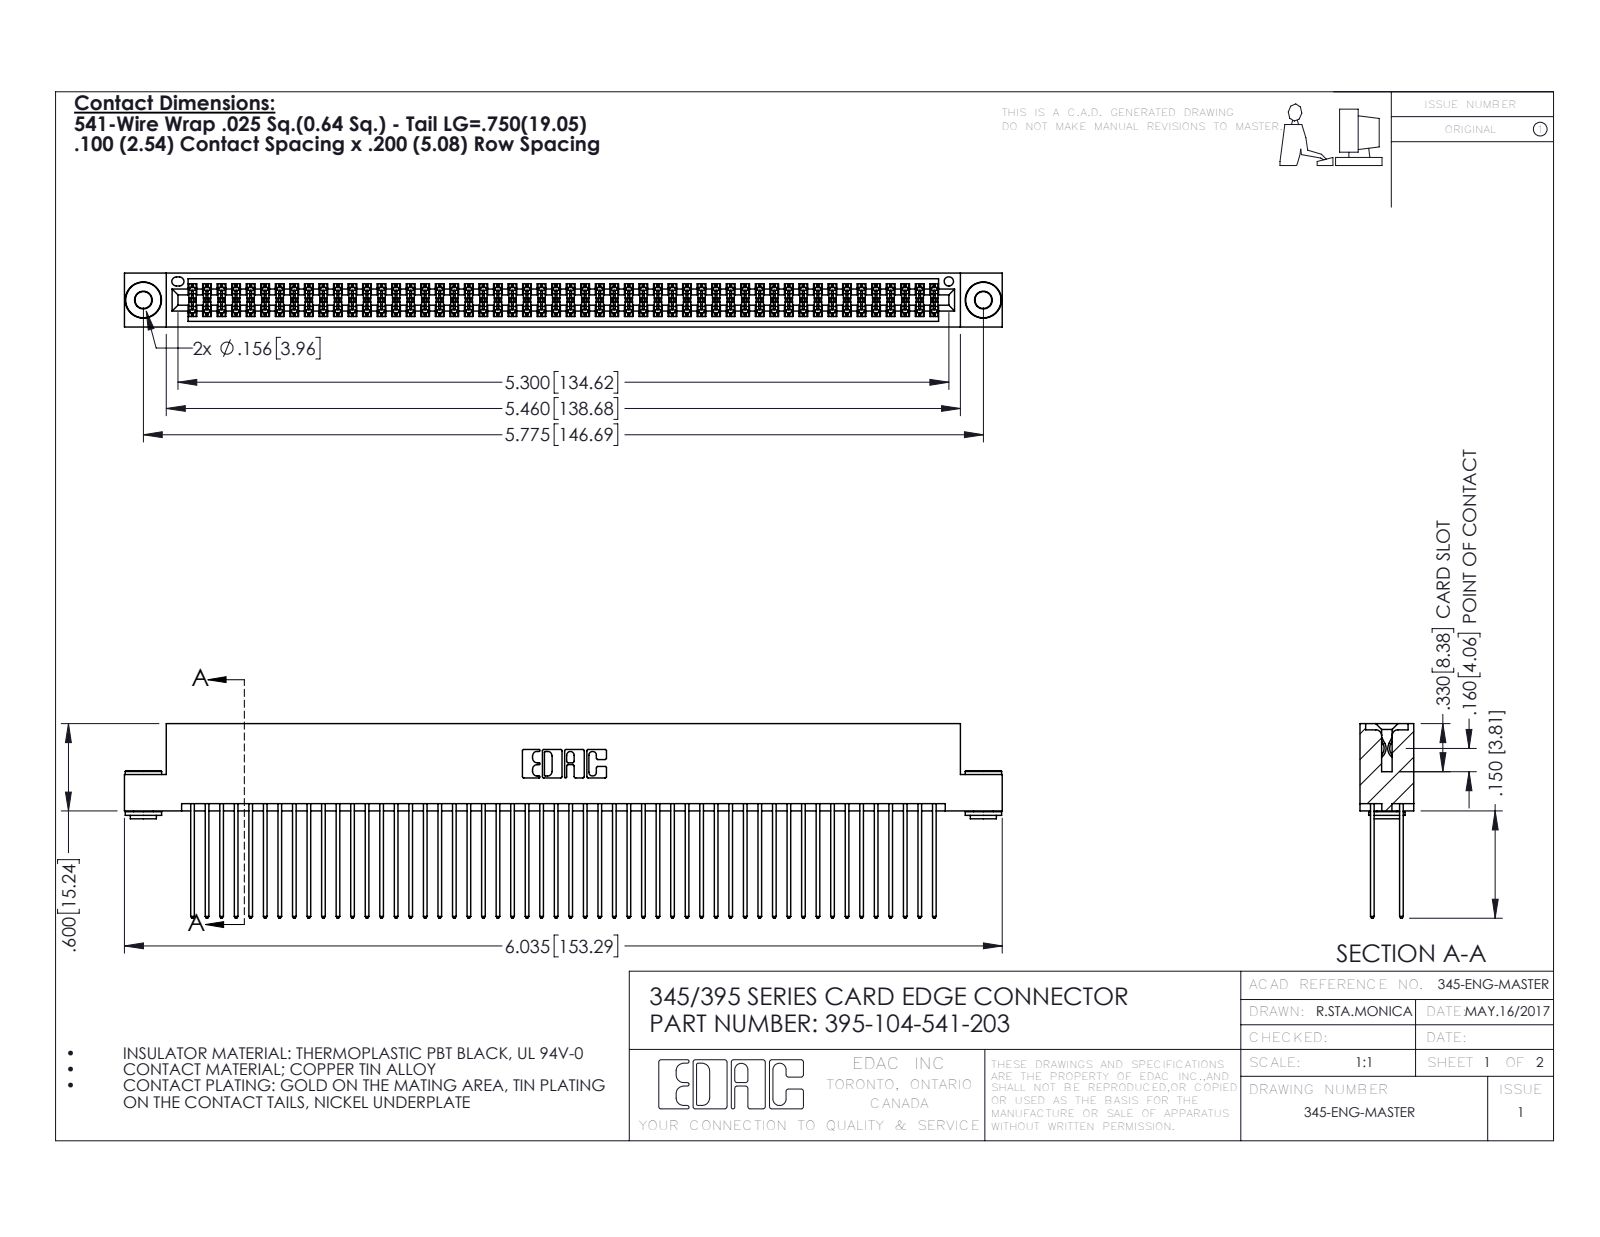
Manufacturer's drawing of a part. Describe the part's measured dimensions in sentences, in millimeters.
The part is named "345-292-001_345-293-141; 345 Part_Flush Mounting Lugs - 0.156 Dia-TH; 345-250-002_345-250-002-102; 395-104-541-203". Its 3-D file was written by "SolidWorks 2016 (CONFIG_CONTROL_DESIGN)". It is 107 solids with 5364 faces: 3522 planar, 1834 cylindrical and 8 other. Overall it measures 153.3 by 34 by 9.4 millimeters. Its volume is 15 600 cubic millimeters and its surface area 26 260 square millimeters. Round holes: 2 of diameter 2.9, 2 of diameter 4, 1 of diameter 1.6. Round bosses or shafts: 2 of diameter 6.4, 2 of diameter 4.6, 2 of diameter 3.5. Partial cylindrical surfaces (rounded edges, fillets, slot ends): 156 of radius 0.2, 104 of radius 0.3, 22 of radius 0.3, 6 of radius 0.2, 6 of radius 0.8, 3 of radius 0.7, 2 of radius 0.4, 2 of radius 0.5. The main face-to-face distances are 1.8, 7.6, 5.1, 0.6, 2.5, 6.9, 5.7, 9.4, 4.4, 3.8. The hole center spacings are 6.9, 140.7, 146.7.
